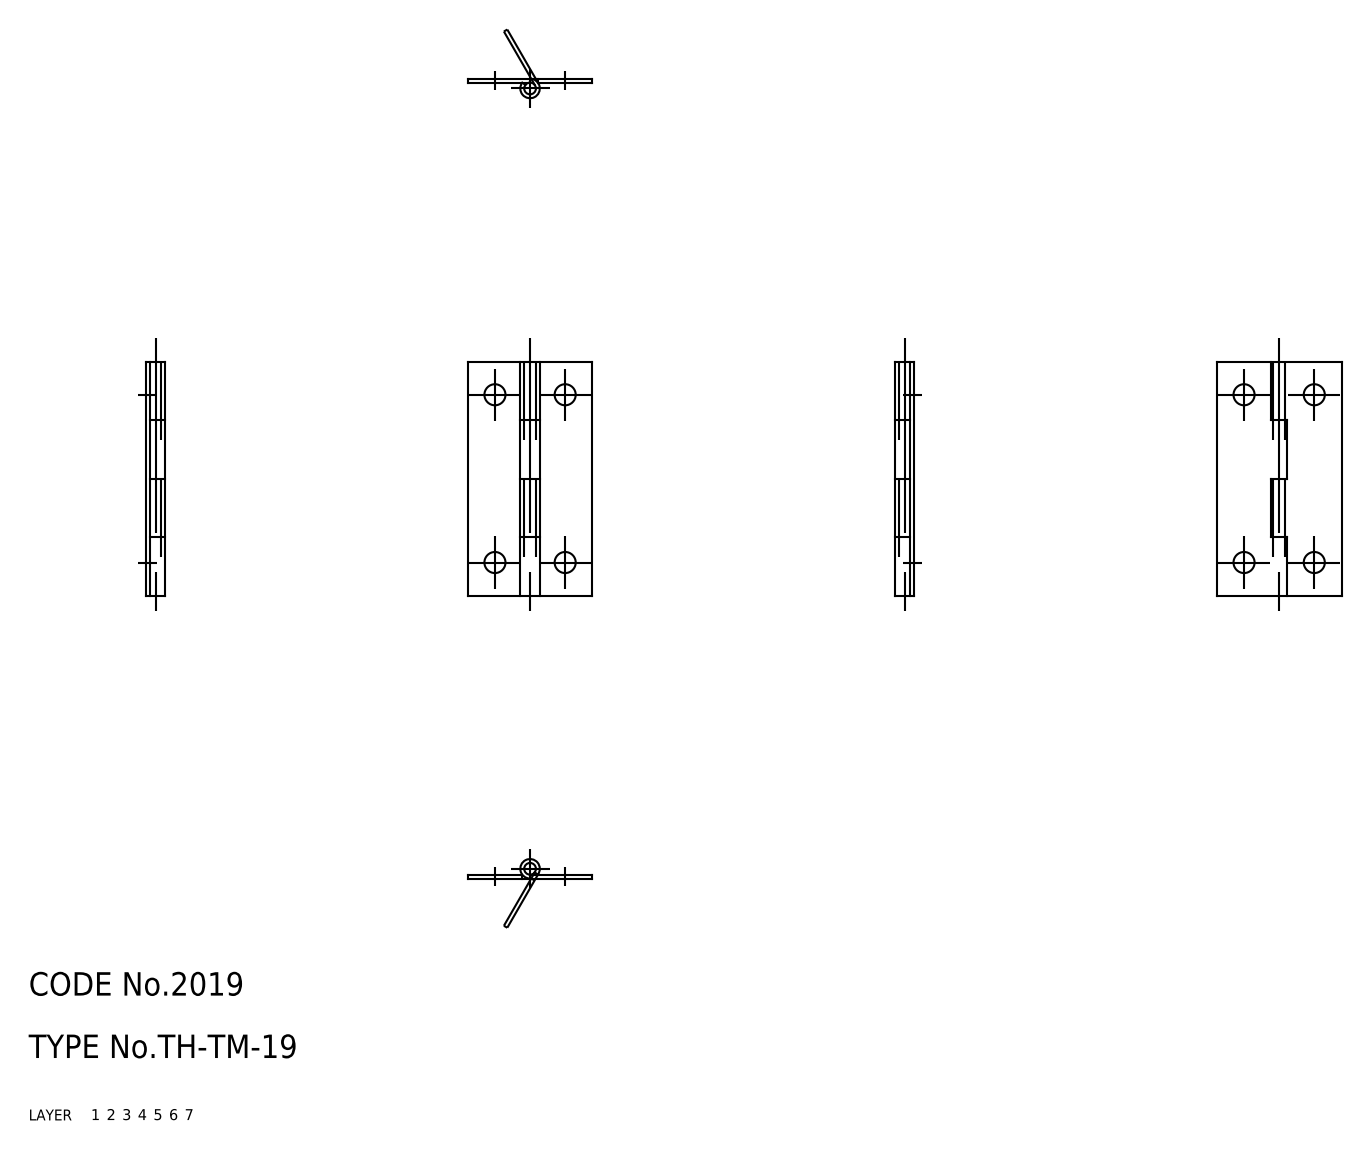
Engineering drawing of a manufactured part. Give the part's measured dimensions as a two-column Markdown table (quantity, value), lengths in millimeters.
| quantity | value |
| --- | --- |
| part name | hinge piece_B; hinge piece_A; shaft; TH_TM_19_21840_36 |
| STEP written by | CADfix (AUTOMOTIVE_DESIGN) |
| units | millimeters |
| bodies | 3 solids, 44 faces (0 planar, 0 cylindrical, 44 other) |
| overall size | 30 × 16 × 2.5 |
| volume | 342 mm³ |
| surface area | 1 419 mm² |
